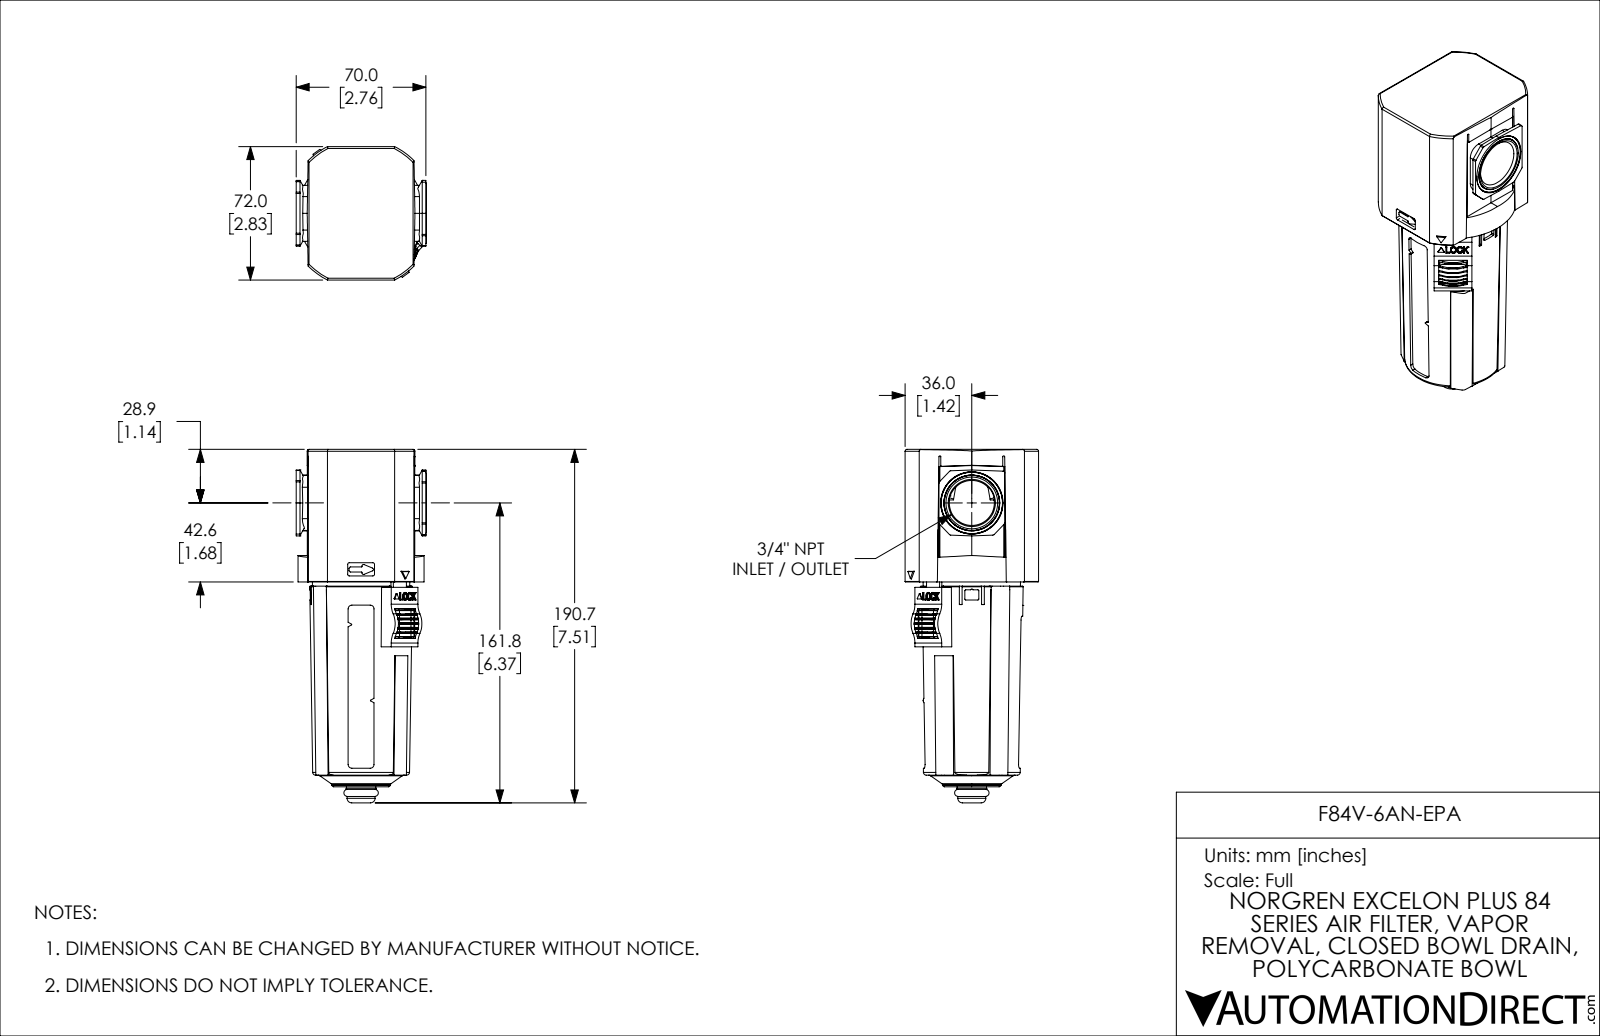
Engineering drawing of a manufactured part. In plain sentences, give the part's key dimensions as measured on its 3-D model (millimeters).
The part is named "F84V-6AN-EPA". Its 3-D file was written by "SolidWorks 2021 (CONFIG_CONTROL_DESIGN)". It is 5 solids with 994 faces: 438 planar, 366 cylindrical and 190 other. Overall it measures 190.7 by 72 by 70.3 millimeters. Its volume is 446 100 cubic millimeters and its surface area 95 100 square millimeters. Round holes: 2 of diameter 4.1, 1 of diameter 3.2, 1 of diameter 6.8, 1 of diameter 24.6, 1 of diameter 62.5. Round bosses or shafts: 2 of diameter 8, 2 of diameter 7, 1 of diameter 23, 1 of diameter 15.9, 1 of diameter 15.1, 1 of diameter 10.1. Partial cylindrical surfaces (rounded edges, fillets, slot ends): 40 of radius 0.5, 32 of radius 1, 24 of radius 0.3, 16 of radius 0.7, 10 of radius 0.2, 8 of radius 1, 8 of radius 1.1, 8 of radius 1.5. The main face-to-face distances are 1.5, 59.7, 61.2, 72, 0.9, 58.9, 60.4, 70, 10.3, 11.2. The hole center spacings are 15.1, 30.2.
